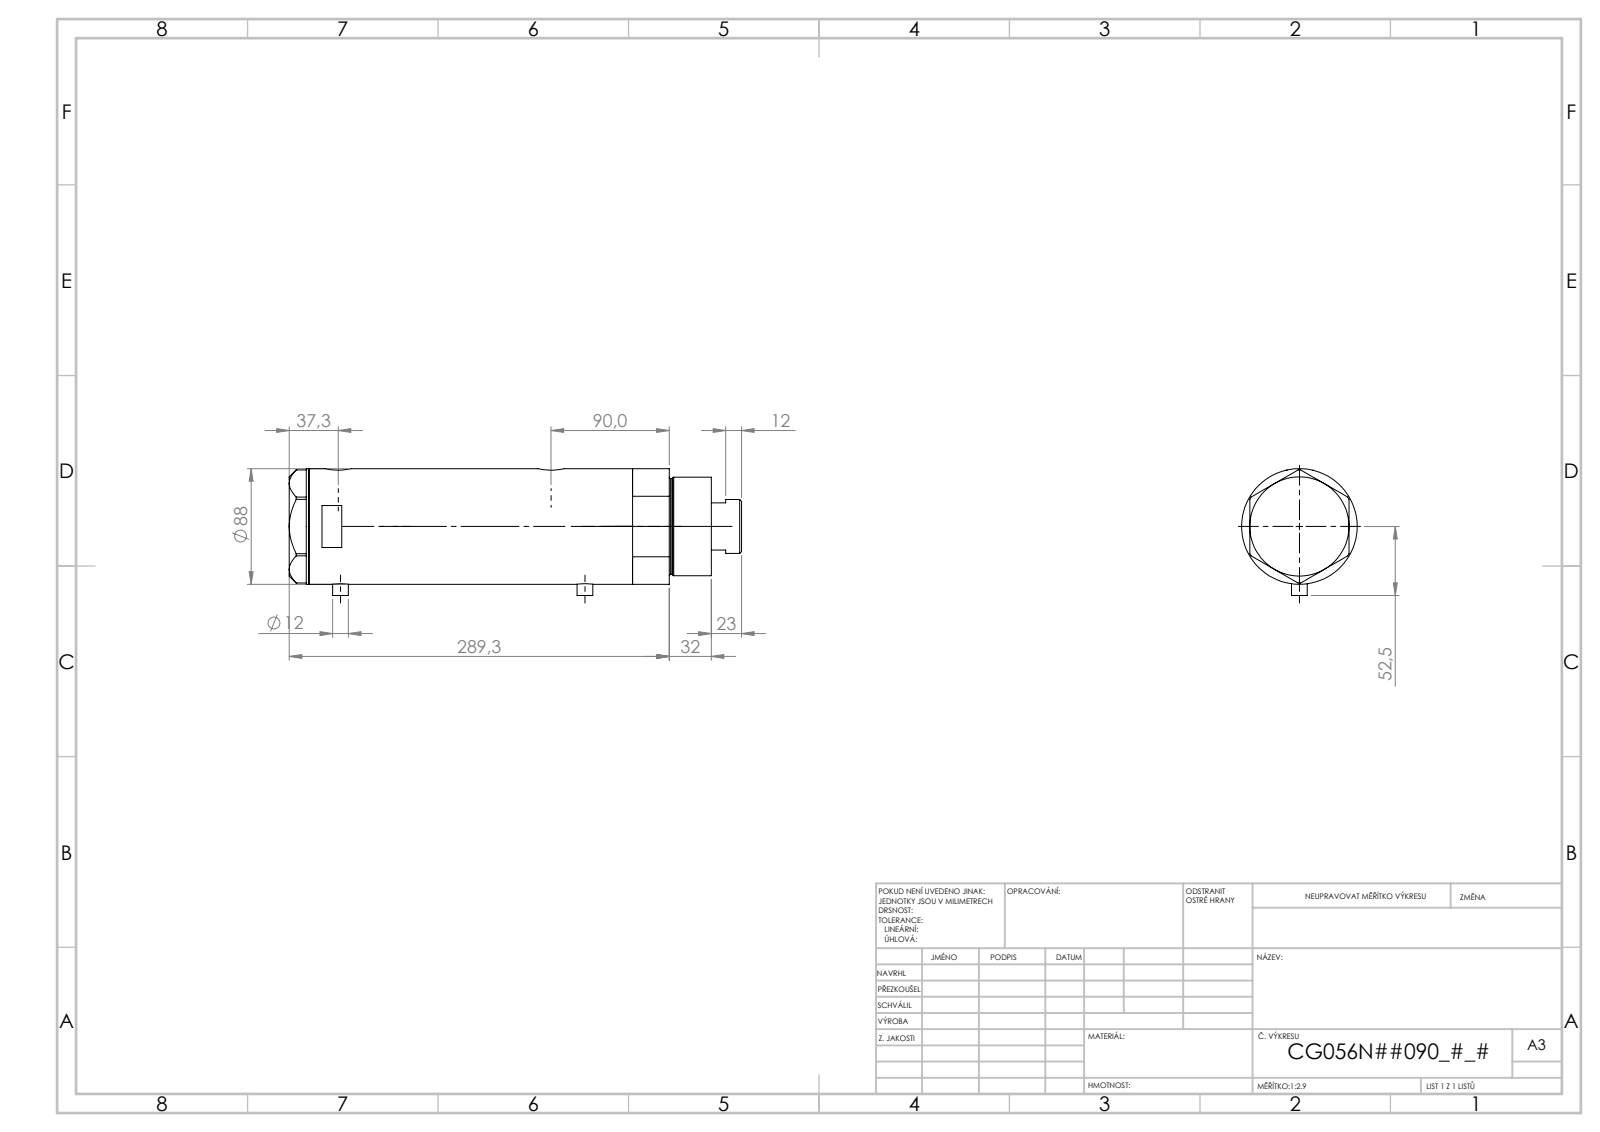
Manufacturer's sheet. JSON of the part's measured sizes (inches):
{"part_name": "V270CG_VC; V270CG_FRONT; V270CG_BACK; V270CG_MIDDLE", "step_written_by": "SolidWorks 2019 (CONFIG_CONTROL_DESIGN)", "units": "inches", "bodies": {"solids": 4, "faces": 126, "planar": 53, "cylindrical": 53, "other": 20}, "overall_size": [12.381, 3.508, 3.465], "volume_in3": 98.37, "surface_area_in2": 360.9, "round_holes": [[0.197, 2], [0.492, 2], [0.518, 2], [0.787, 2], [0.571, 1], [1.654, 1], [1.713, 1], [2.205, 1], [2.362, 1], [3.15, 1]], "round_bosses_or_shafts": [[0.472, 2], [3.465, 1], [2.953, 1], [2.874, 1], [1.614, 1]], "face_to_face_distances": [6.472, 1.024, 5.449, 0.591, 1.614, 7.063, 10.885, 11.475, 9.861, 4.412], "hole_center_spacings": [0.067, 1.016, 5.524, 5.591, 6.539, 6.606]}
